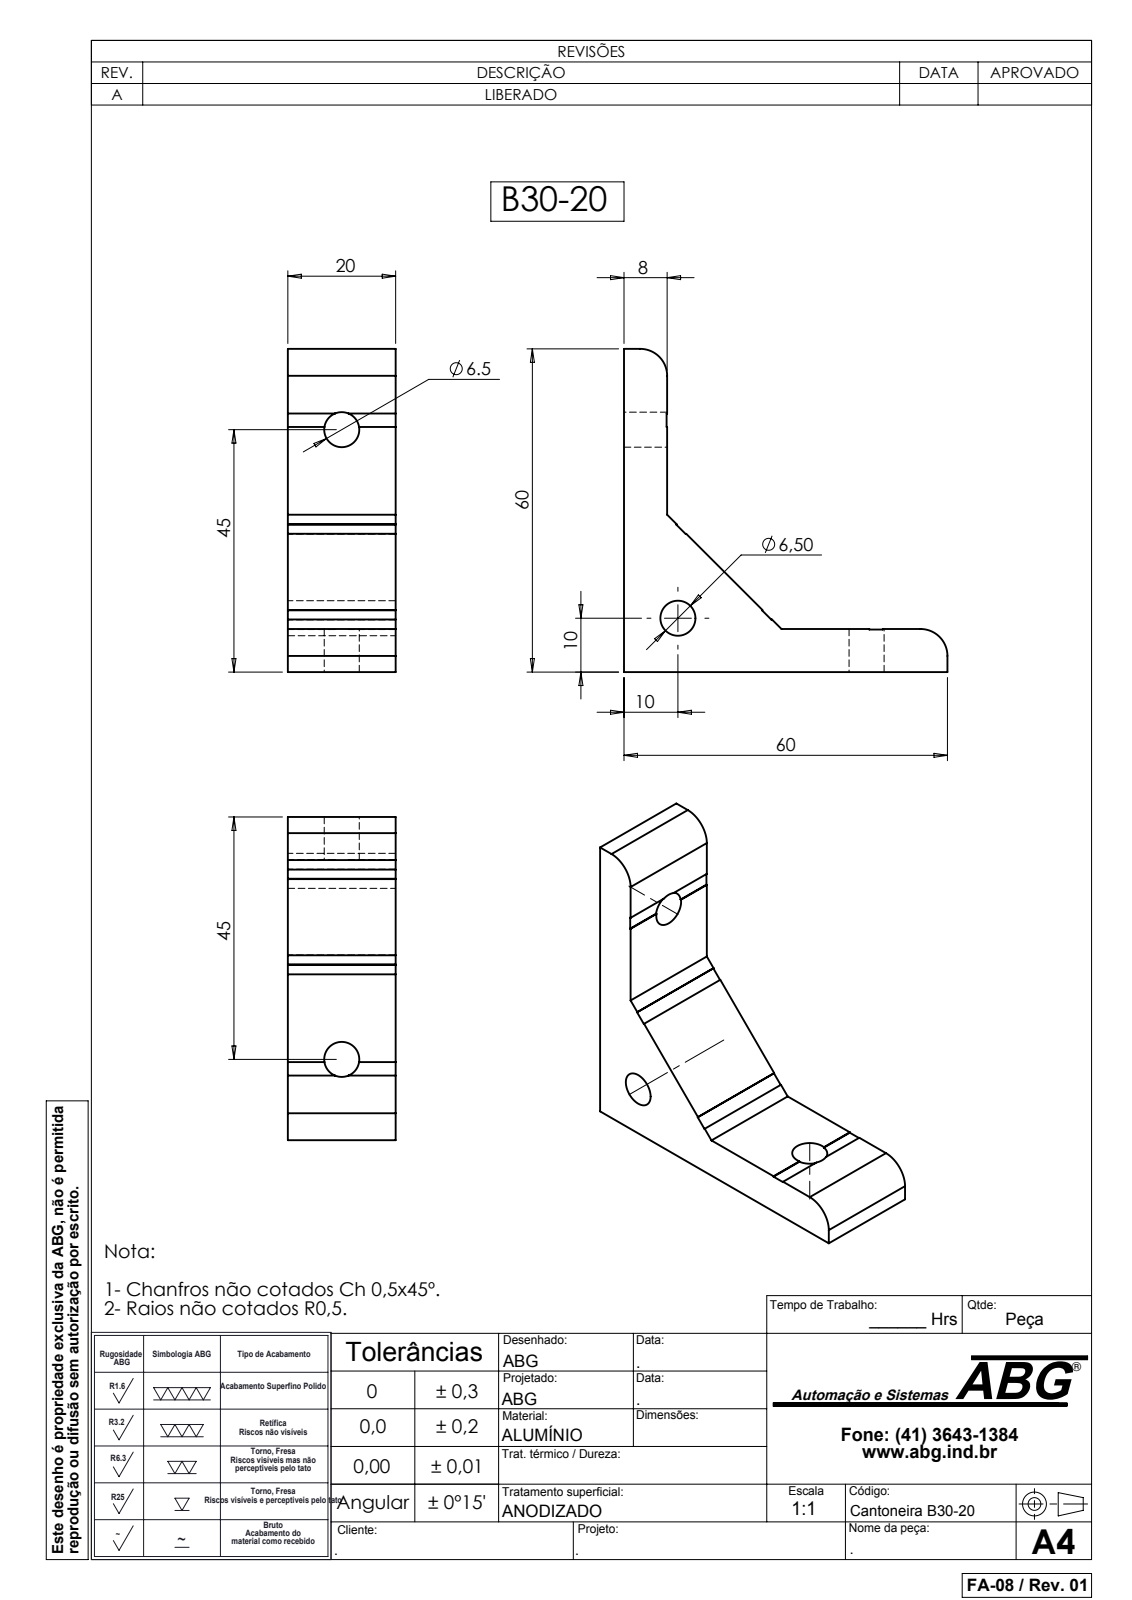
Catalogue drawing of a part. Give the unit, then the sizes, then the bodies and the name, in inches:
Units: inches
Overall size (bounding box): 2.362 × 2.362 × 0.787
Round holes (diameter × count): ⌀0.256 ×3
Partial cylindrical surfaces — rounded edges, fillets, slot ends (radius × count): R0.197 ×2
Main face-to-face distances: 0.787, 0.315, 2.047, 2.362, 2.051, 0.311, 0.098, 0.886, 0.472, 1.575
Volume: 1.281 in³ · Surface area: 11.21 in²
Bodies: 1 solid, 39 faces (31 planar, 8 cylindrical, 0 other)
Part name (STEP PRODUCT): B30-20
STEP written by: SolidWorks 2007 (CONFIG_CONTROL_DESIGN)
